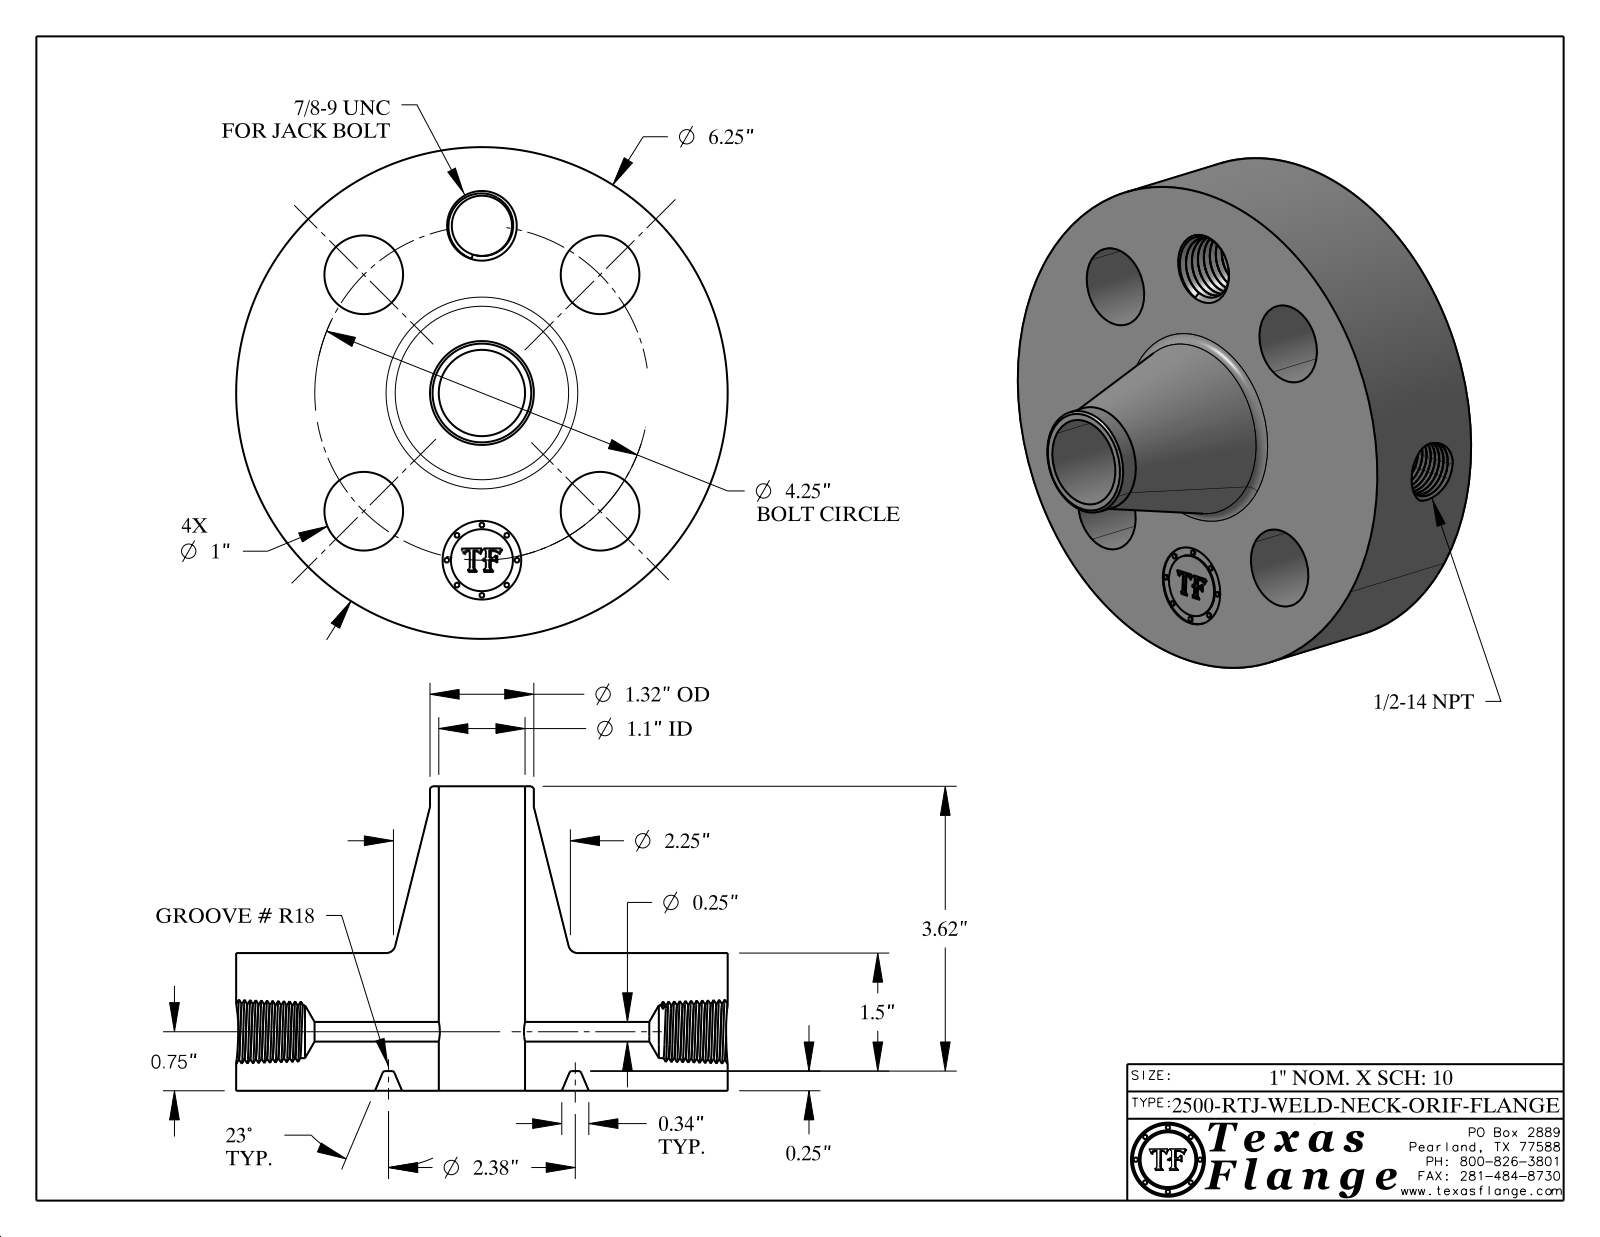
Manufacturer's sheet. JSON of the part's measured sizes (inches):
{"part_name": "2500-RTJ-WELD-NECK", "step_written_by": "CATIA V5 STEP AP214 (AUTOMOTIVE_DESIGN)", "units": "inches", "bodies": {"solids": 1, "faces": 773, "planar": 370, "cylindrical": 85, "other": 318}, "overall_size": [6.25, 6.25, 3.87], "volume_in3": 47.35, "surface_area_in2": 148.9, "round_holes": [[1, 5], [0.25, 1], [0.672, 1], [0.766, 1], [1.097, 1]], "round_bosses_or_shafts": [[0.061, 8], [6.25, 1], [1.32, 1], [0.788, 1]], "face_to_face_distances": [1.75, 0.25, 1.5, 0.015, 1.735, 1.485, 3.87, 3.62, 2.135, 2.12], "hole_center_spacings": [2.125, 1.626, 3.006, 3.927, 4.25]}
